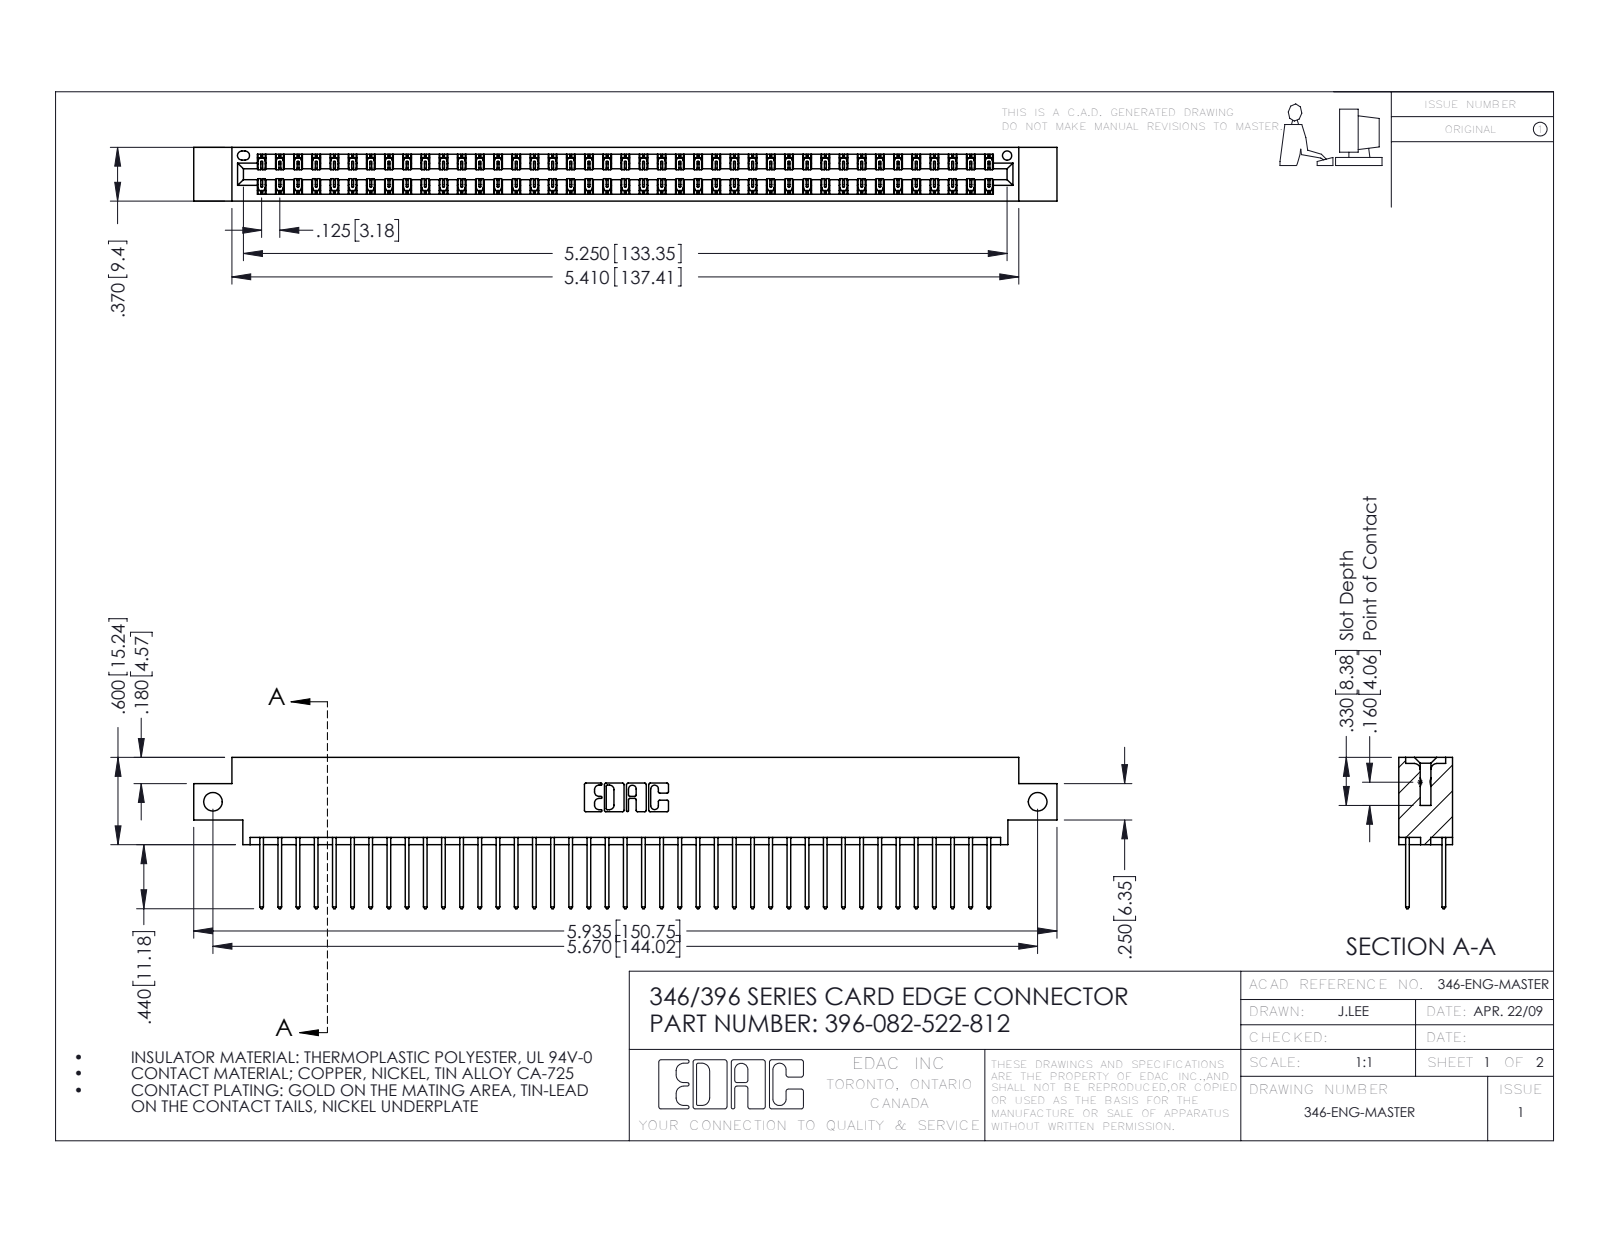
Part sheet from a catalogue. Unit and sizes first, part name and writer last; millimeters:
Units: millimetres
Overall size (bounding box): 150.7 × 26.4 × 9.4
Round holes (diameter × count): ⌀3.3 ×2, ⌀1.6 ×1
Partial cylindrical surfaces — rounded edges, fillets, slot ends (radius × count): R0.2 ×123, R0.3 ×82, R0.3 ×22, R0.2 ×6, R0.8 ×6, R0.7 ×3, R0.4 ×2, R0.6 ×2
Main face-to-face distances: 1.2, 8.2, 6.4, 9.4, 1.8, 7.6, 0.6, 7, 3.8, 5.6
Hole centre spacings: 144
Volume: 14 700 mm³ · Surface area: 21 150 mm²
Bodies: 83 solids, 4390 faces (2950 planar, 1440 cylindrical, 0 other)
Part name (STEP PRODUCT): 396-082-522-812; 346 Part_0.170 Offset - Side Mount; 345-292-001_345-293-122
STEP written by: SolidWorks 2016 (CONFIG_CONTROL_DESIGN)
